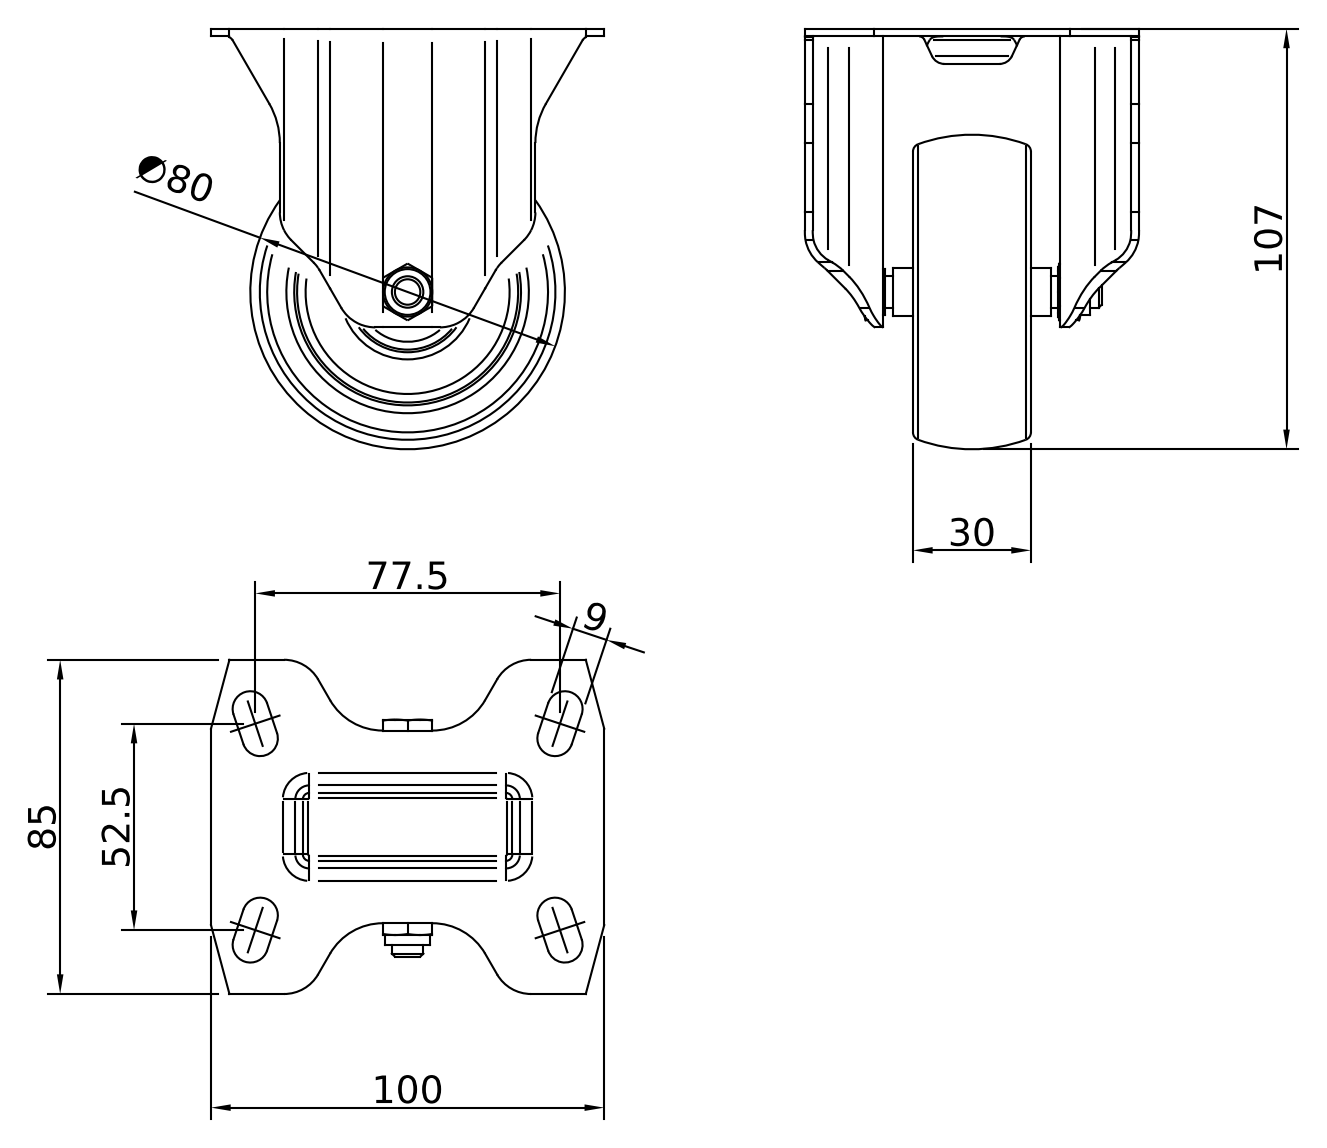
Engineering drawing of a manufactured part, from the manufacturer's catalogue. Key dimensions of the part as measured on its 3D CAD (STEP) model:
Part name (STEP PRODUCT): CRUST0000021; 440000025922; 440000025921; 440000025920
STEP written by: Autodesk Inventor 2022 (AUTOMOTIVE_DESIGN)
Units: millimetres
Bodies: 3 solids, 220 faces (93 planar, 73 cylindrical, 54 other)
Overall size (bounding box): 107 × 100 × 85
Volume: 138 682 mm³ · Surface area: 61 949 mm²
Round holes (diameter × count): ⌀12 ×1
Round bosses / shafts (diameter × count): ⌀11.63 ×1, ⌀8 ×1
Partial cylindrical surfaces — rounded edges, fillets, slot ends (radius × count): R10 ×10, R1.5 ×8, R3.5 ×8, R4.5 ×8, R7 ×4, R8 ×4, R15.5 ×4, R17.5 ×4
Main face-to-face distances: 2, 7.5, 9.5, 65, 39.5, 18, 47, 37.5, 7, 3.92
